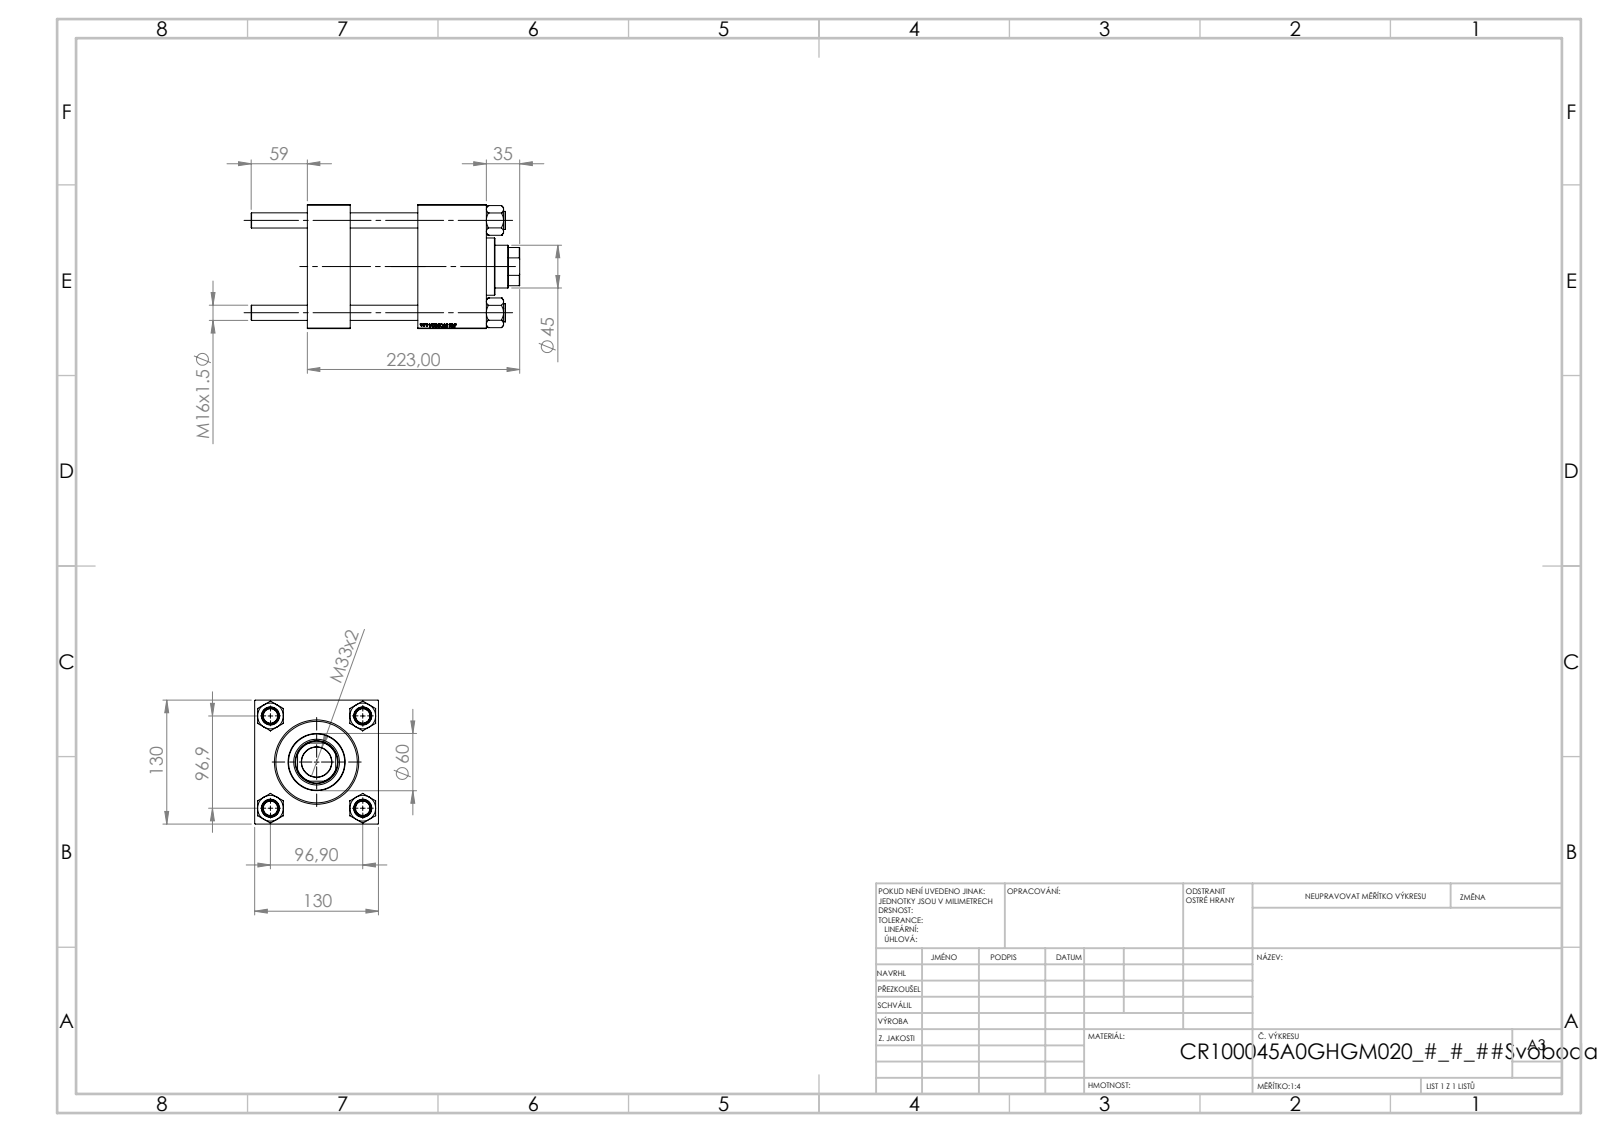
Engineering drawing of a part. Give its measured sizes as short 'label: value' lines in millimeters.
name: NUT_M5; V215_VC_A; CR025_012_A_0_G_A_G_M_020_+#_##_TYCINKA; V215CR_VCP (+1 more)
written by: SolidWorks 2019 (CONFIG_CONTROL_DESIGN)
unit: mm
bodies: 11 solids, 1182 faces (568 planar, 78 cylindrical, 536 other)
size: 282 × 130 × 130
volume: 2 505 000 mm³; area: 353 611 mm²
holes: 4× ⌀16, 2× ⌀7, 2× ⌀26.44, 2× ⌀35, 1× ⌀31.5, 1× ⌀45, 1× ⌀48, 1× ⌀76, 1× ⌀85.5, 1× ⌀100
bosses: 4× ⌀19, 1× ⌀106, 1× ⌀60
rounds: 1× R22
face distances: 130, 45, 188, 143, 116, 71, 72, 20, 92, 96
hole spacings: 68.52, 96.9, 137.04, 118.5
